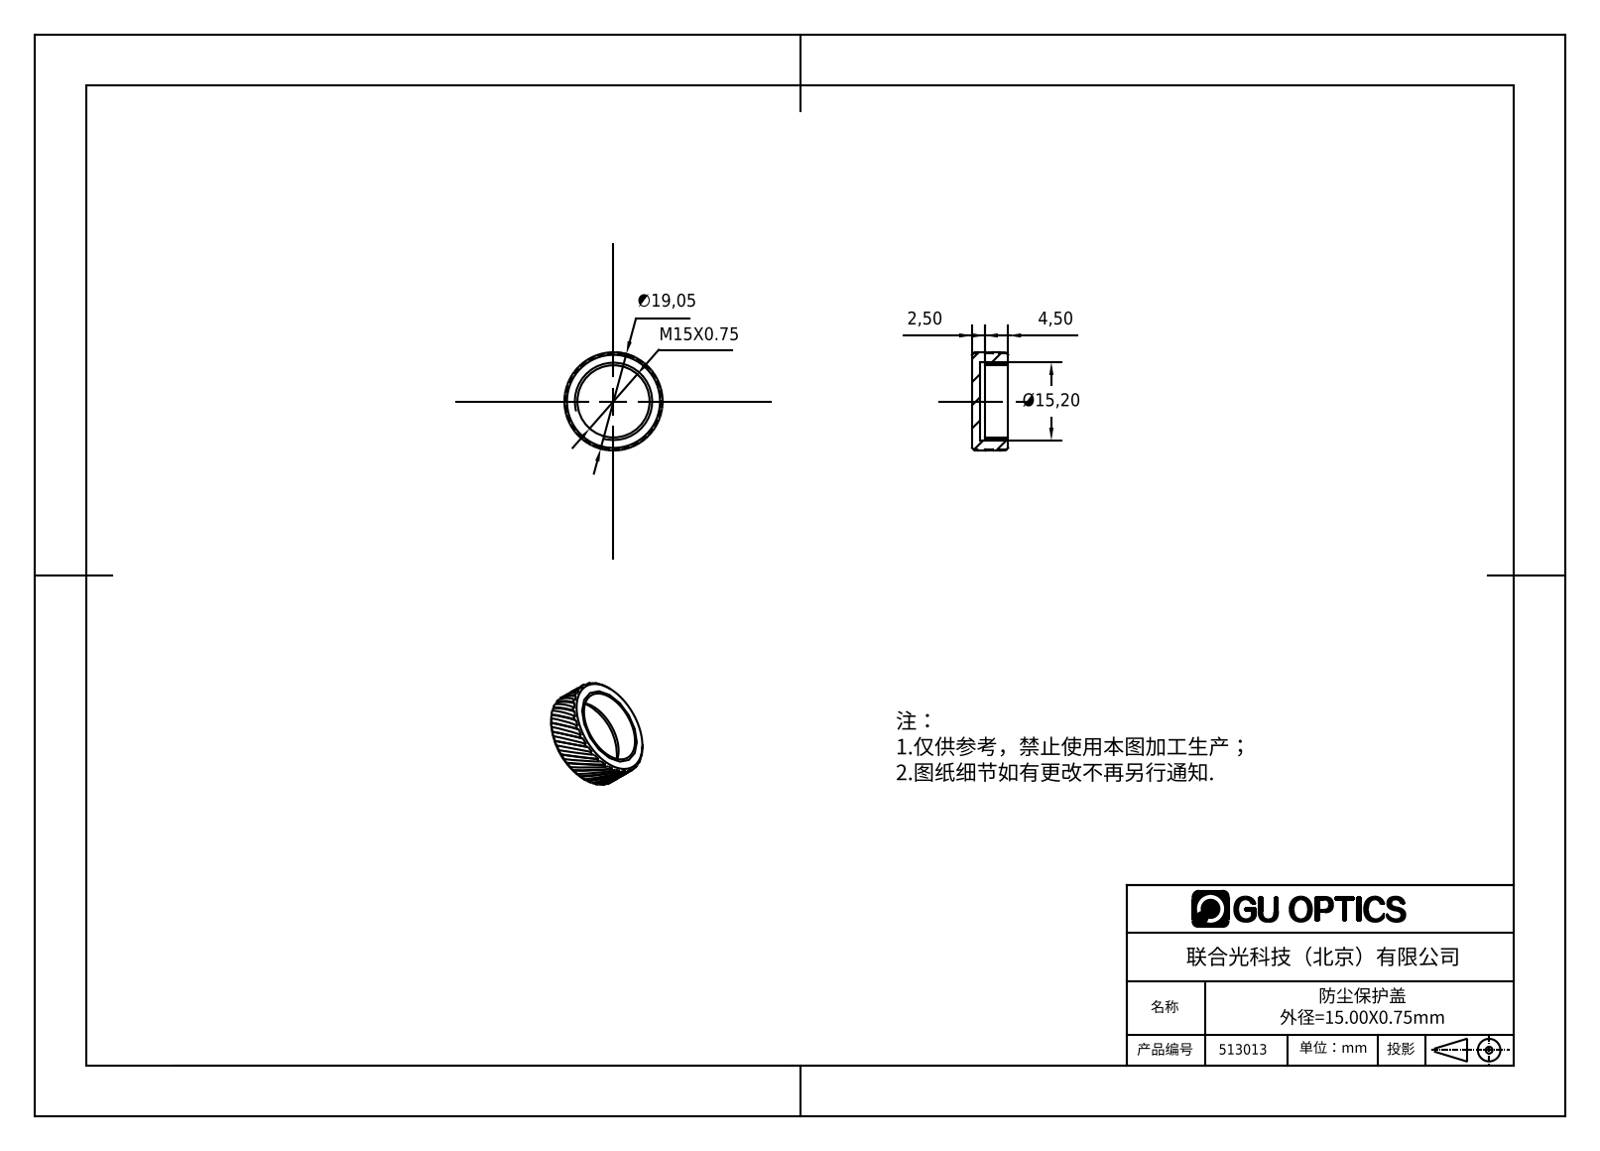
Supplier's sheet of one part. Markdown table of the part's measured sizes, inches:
| quantity | value |
| --- | --- |
| part name | 513013 |
| STEP written by | SolidWorks 2016 (AUTOMOTIVE_DESIGN) |
| units | inches |
| bodies | 1 solid, 134 faces (64 planar, 66 cylindrical, 4 other) |
| overall size | 0.75 × 0.75 × 0.276 |
| volume | 0.065 in³ |
| surface area | 2.089 in² |
| round holes (diameter × count) | 0.551 × 1, 0.598 × 1 |
| round bosses / shafts (diameter × count) | 0.75 × 1, 0.734 × 1 |
| main face-to-face distances | 0.059, 0.217, 0.276, 0.031, 0.177, 0.039, 0.098 |
